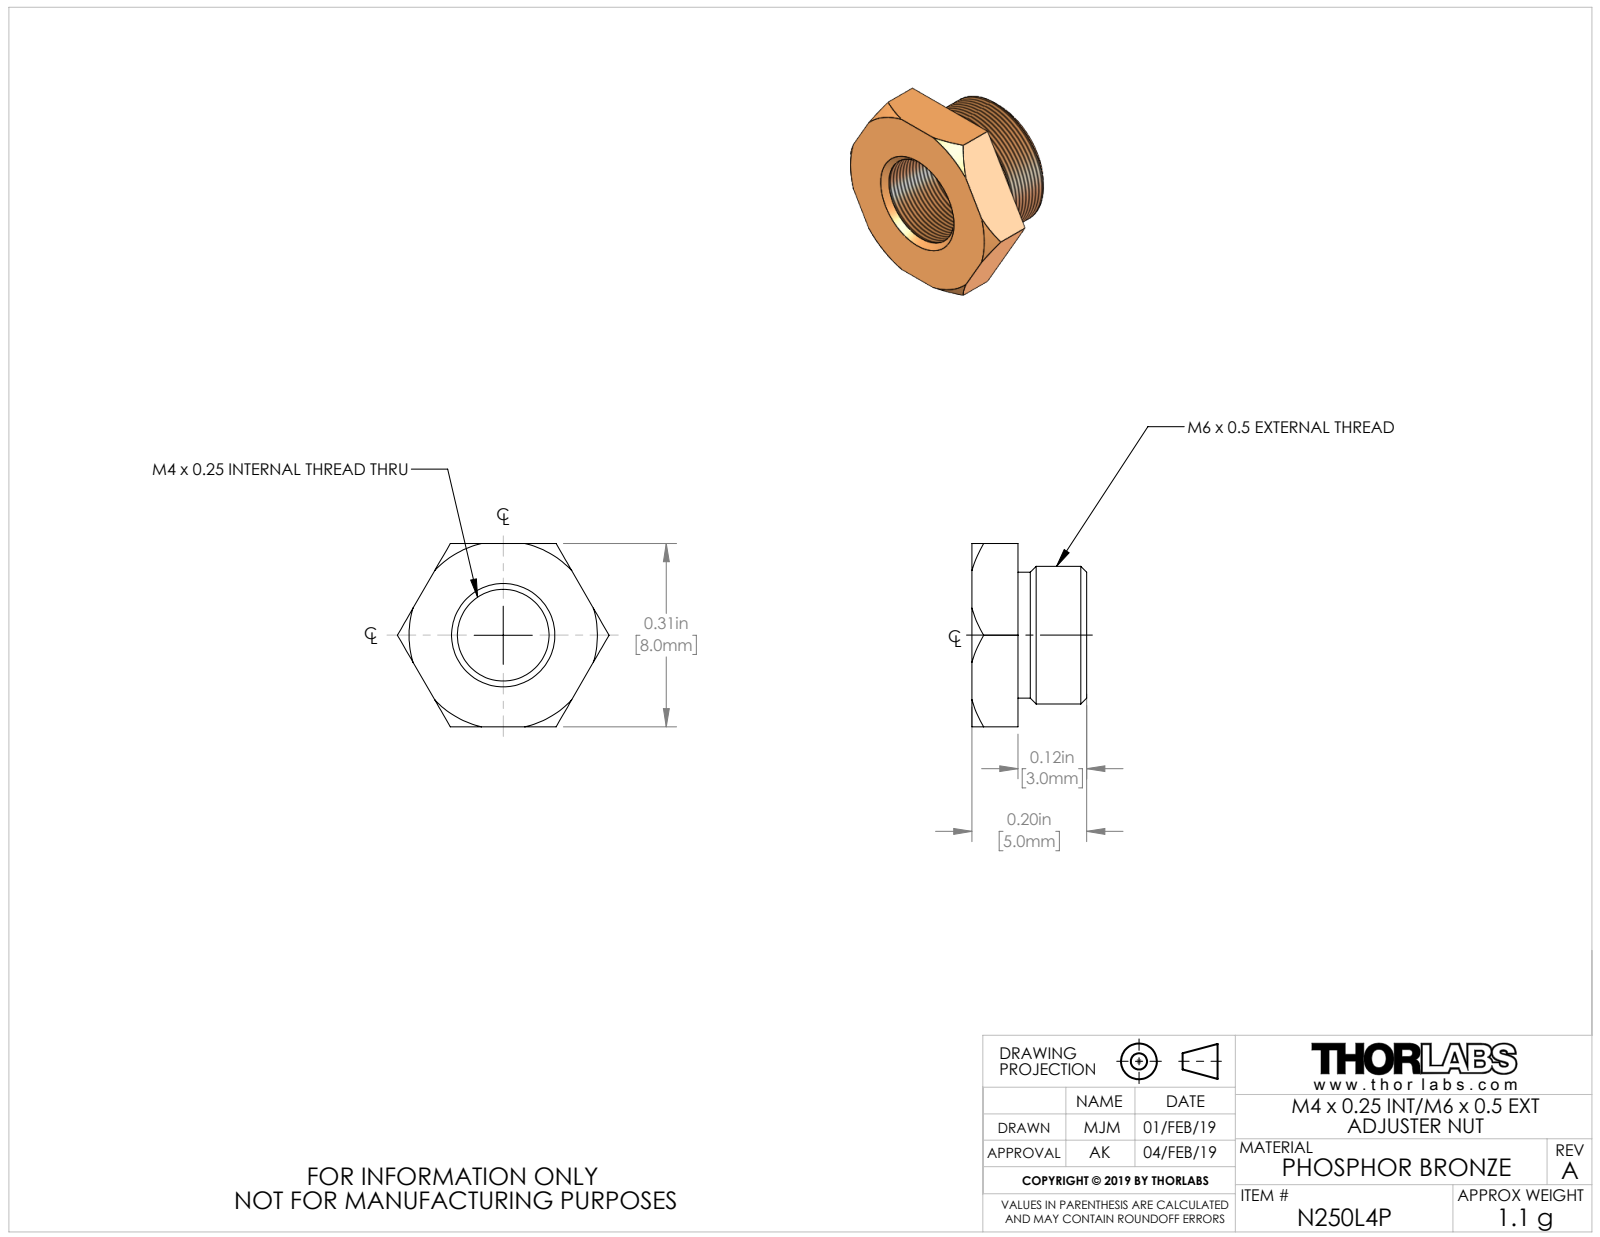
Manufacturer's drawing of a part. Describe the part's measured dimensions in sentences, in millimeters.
The part is named "TTN174839-E0W". Its 3-D file was written by "SolidWorks 2018 (AUTOMOTIVE_DESIGN)". It is 1 solid with 29 faces: 9 planar, 6 cylindrical and 14 other. Overall it measures 9.2 by 8 by 5 millimeters. Its volume is 100 cubic millimeters and its surface area 257 square millimeters. Round holes: 1 of diameter 4. Round bosses or shafts: 1 of diameter 6, 1 of diameter 5.5. The main face-to-face distances are 2, 8, 3, 5.
